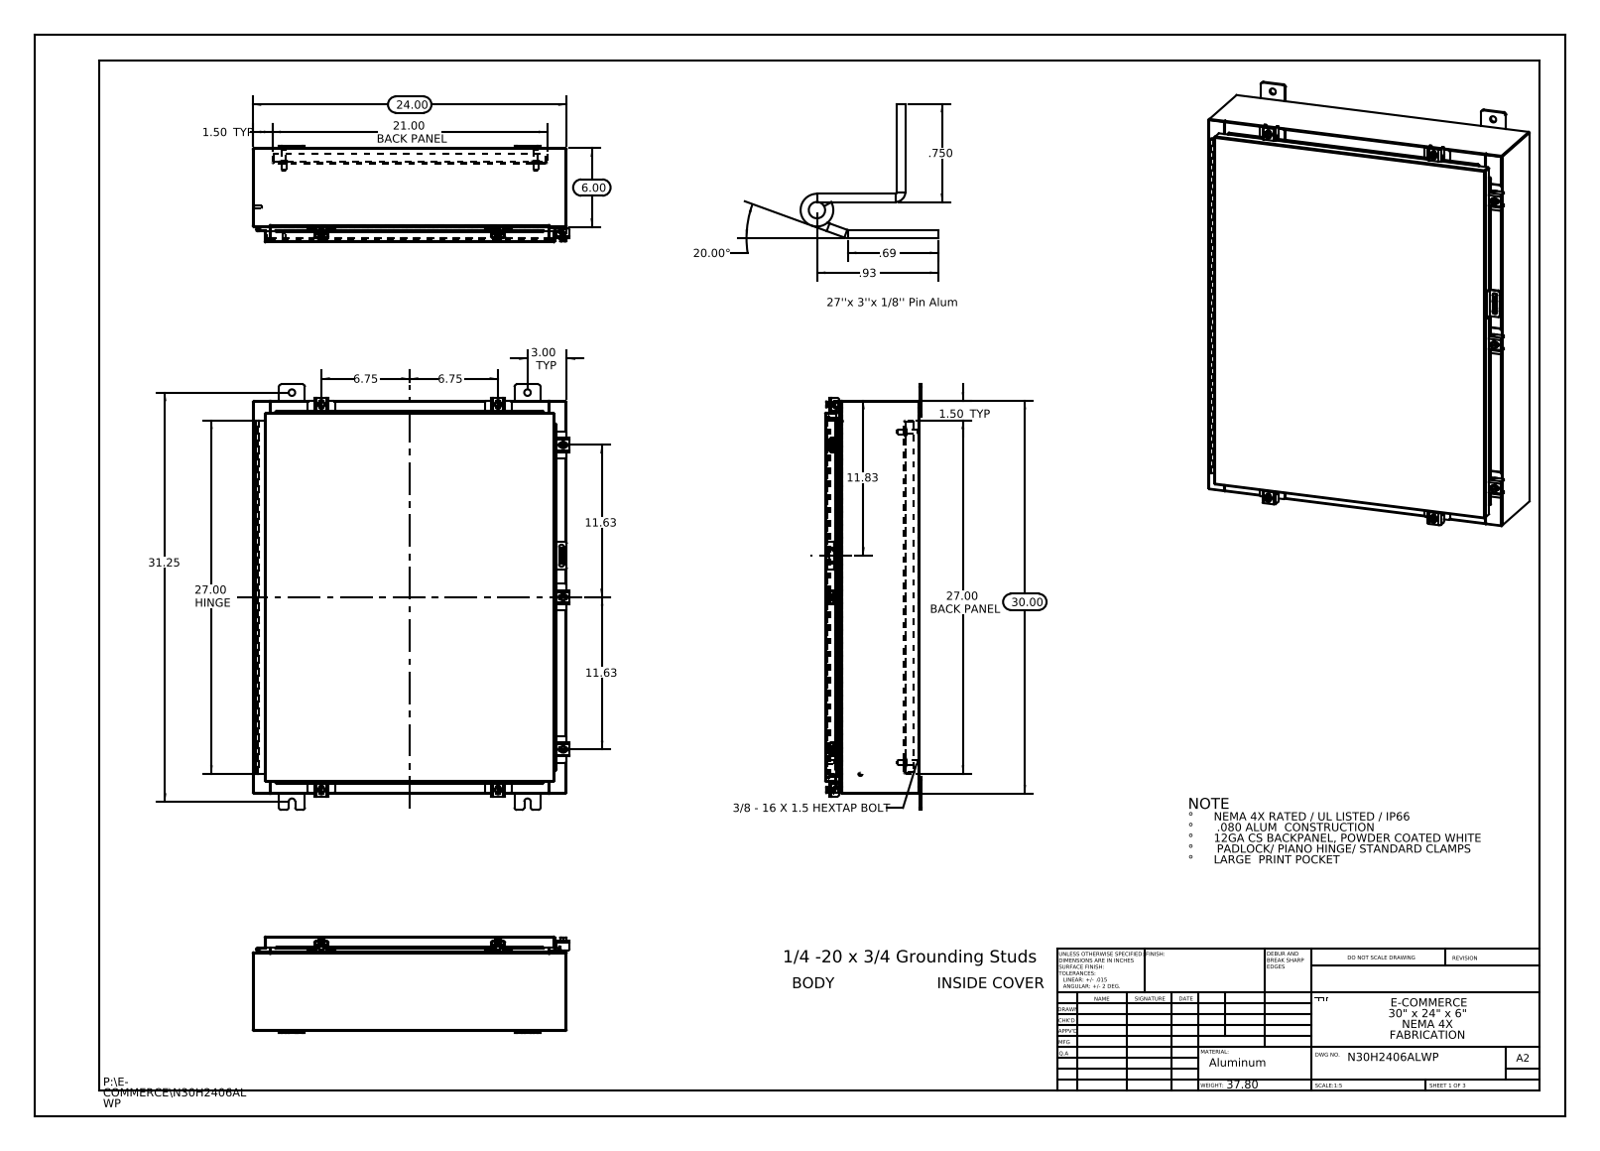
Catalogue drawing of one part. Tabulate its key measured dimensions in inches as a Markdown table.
| quantity | value |
| --- | --- |
| part name | N30H2406ALWP Clamp Assembly; N30H2406ALWP Cover; N30H2406ALWP Bottom; N30H2406ALWP Padlock Staple (+8 more) |
| STEP written by | SolidWorks 2013 (CONFIG_CONTROL_DESIGN) |
| units | inches |
| bodies | 54 solids, 2016 faces (1062 planar, 838 cylindrical, 116 other) |
| overall size | 32.5 × 24.211 × 7.389 |
| volume | 248.8 in³ |
| surface area | 6 189 in² |
| round holes (diameter × count) | 0.5 × 8, 0.213 × 7, 0.26 × 7, 0.125 × 2, 0.125 × 1 |
| round bosses / shafts (diameter × count) | 0.25 × 8, 0.5 × 7, 0.399 × 7, 0.625 × 4, 0.375 × 4, 0.33 × 4, 0.315 × 2, 0.236 × 2 |
| partial cylindrical surfaces (radius × count) | 0.06 × 34, 0.013 × 27, 0.19 × 24, 0.088 × 21, 0.12 × 14, 0.141 × 14, 0.05 × 11, 0.08 × 10 |
| main face-to-face distances | 0.075, 7.126, 7.051, 7.201, 0.104, 1, 1.075, 6.051, 6.126, 1.179 |
| hole center spacings | 27.501, 31.878, 1.858, 2.277, 2.326, 2.423, 3.561, 3.561 |
